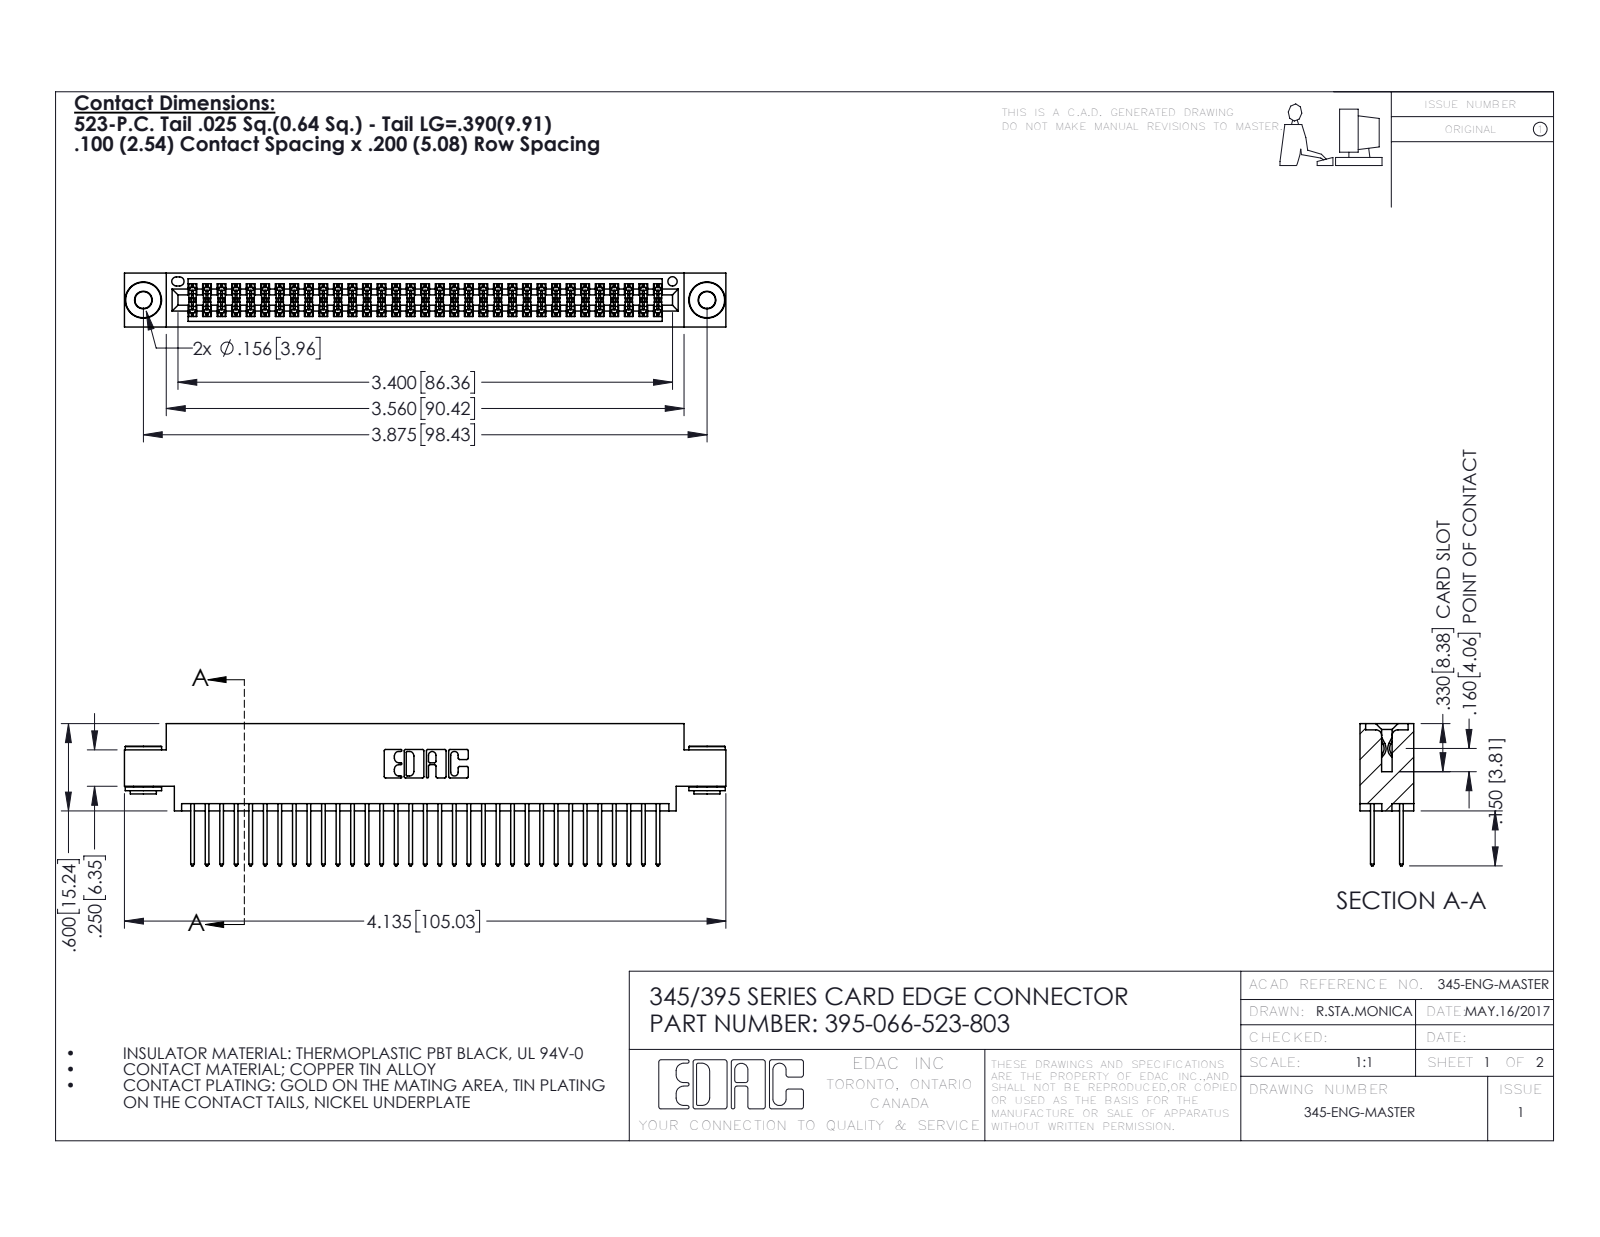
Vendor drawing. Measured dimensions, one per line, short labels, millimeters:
name: 345 Part_0.170 Offset - 0.156 Dia-TH; 395-066-523-803; 345-250-002_345-250-002-102; 345-292-001_345-293-123
written by: SolidWorks 2016 (CONFIG_CONTROL_DESIGN)
unit: mm
bodies: 69 solids, 3468 faces (2272 planar, 1188 cylindrical, 8 other)
size: 105 × 24.8 × 9.4
volume: 10 200 mm³; area: 15 800 mm²
holes: 2× ⌀2.9, 2× ⌀4, 1× ⌀1.6
bosses: 2× ⌀6.4, 2× ⌀4.6, 2× ⌀3.5
rounds: 99× R0.2, 66× R0.3, 22× R0.3, 6× R0.2, 6× R0.8, 3× R0.7, 2× R0.4, 2× R0.5
face distances: 1.8, 7.6, 5.1, 2.5, 6.9, 0.6, 9.4, 5.7, 4.4, 3.8
hole spacings: 6.9, 92.5, 98.4
